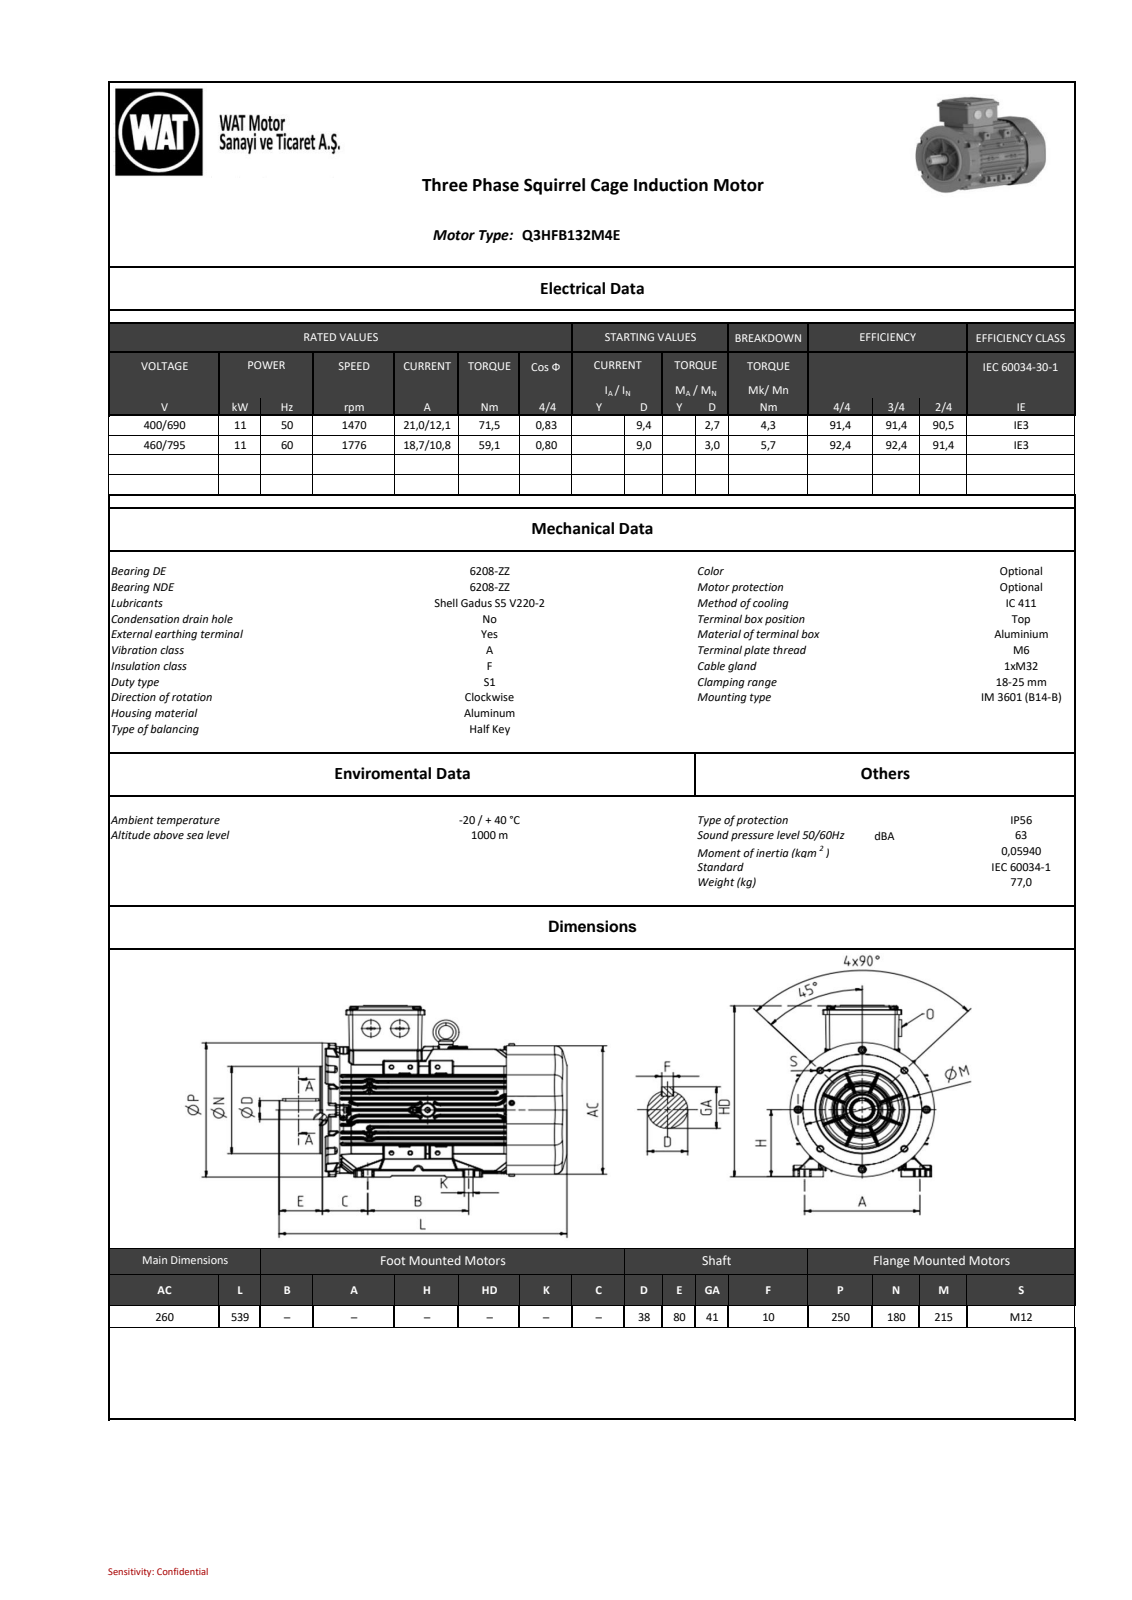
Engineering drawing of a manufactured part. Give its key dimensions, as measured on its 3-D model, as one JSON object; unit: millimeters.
{"part_name": "QH series_ 132_B14b _DEEP COVER__stp_objects", "step_written_by": "SIEMENS PLM Software NX2206.8101 (AP203_CONFIGURATION_CONTROLLED_3D_DESIGN_OF_MECHANICAL_PARTS_AND_ASSEMBLIES_MIM_LF)", "units": "millimeters", "bodies": {"solids": 0, "faces": 7273, "planar": 1827, "cylindrical": 3110, "other": 2336}, "overall_size": [538.95, 320.78, 267.73], "round_holes": [[8.47, 2], [8.48, 2], [6.8, 1], [8, 1], [8.48, 1], [12, 1], [13, 1], [34.5, 1], [62, 1], [82, 1], [180, 1], [225, 1]], "round_bosses_or_shafts": [[8, 8], [13, 4], [38, 3], [230.5, 1], [180, 1], [86.77, 1], [40, 1], [37.4, 1]], "partial_cylinders_radius": [[0.8, 996], [1, 745], [0.5, 158], [3, 64], [2, 62], [1.5, 58], [5, 18], [60, 16]], "face_to_face_distances": [10.42, 1.5, 10.56, 10.28, 20.84, 125.58, 115.18, 104.9, 94.46, 21.12], "hole_center_spacings": [114.16, 0.67, 89.32, 103.84, 125, 143, 147.4, 178.91]}
